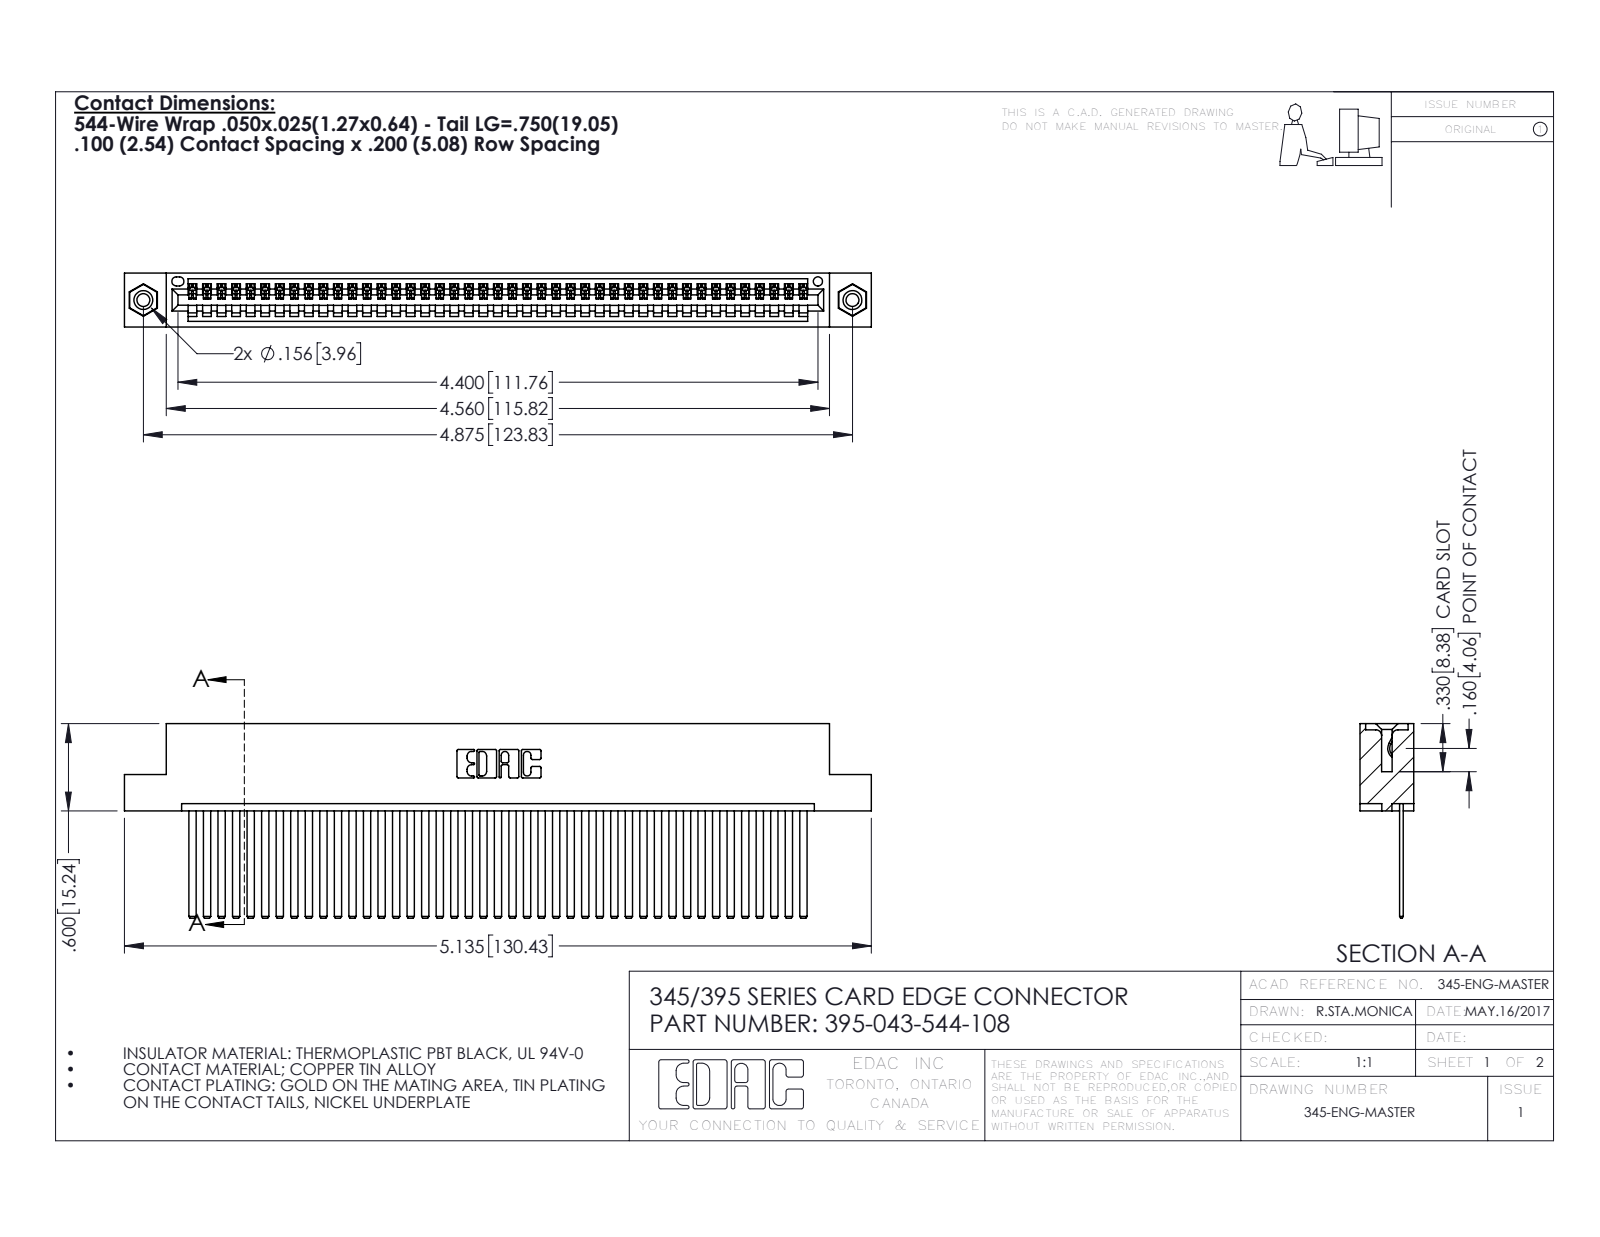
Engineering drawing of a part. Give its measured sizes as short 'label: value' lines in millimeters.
name: 395-043-544-108; 345-250-001_345-250-003-102; 345 Part_Flush Mounting Lugs - 0.156 Dia-TI; 345-292-001_345-293-144
written by: SolidWorks 2016 (CONFIG_CONTROL_DESIGN)
unit: mm
bodies: 46 solids, 2422 faces (1660 planar, 746 cylindrical, 16 other)
size: 130.4 × 34 × 9.4
volume: 12 900 mm³; area: 18 650 mm²
holes: 2× ⌀2.3, 2× ⌀3.2, 2× ⌀4, 1× ⌀1.6
bosses: 2× ⌀3.9
rounds: 86× R0.2, 22× R0.3, 6× R0.2, 6× R0.8, 3× R0.7, 2× R0.8, 2× R1, 1× R0.4
face distances: 1.8, 7.6, 0.6, 2.5, 6.9, 9.4, 5.1, 5.7, 3.8, 1.8
hole spacings: 6.9, 117.8, 123.8
